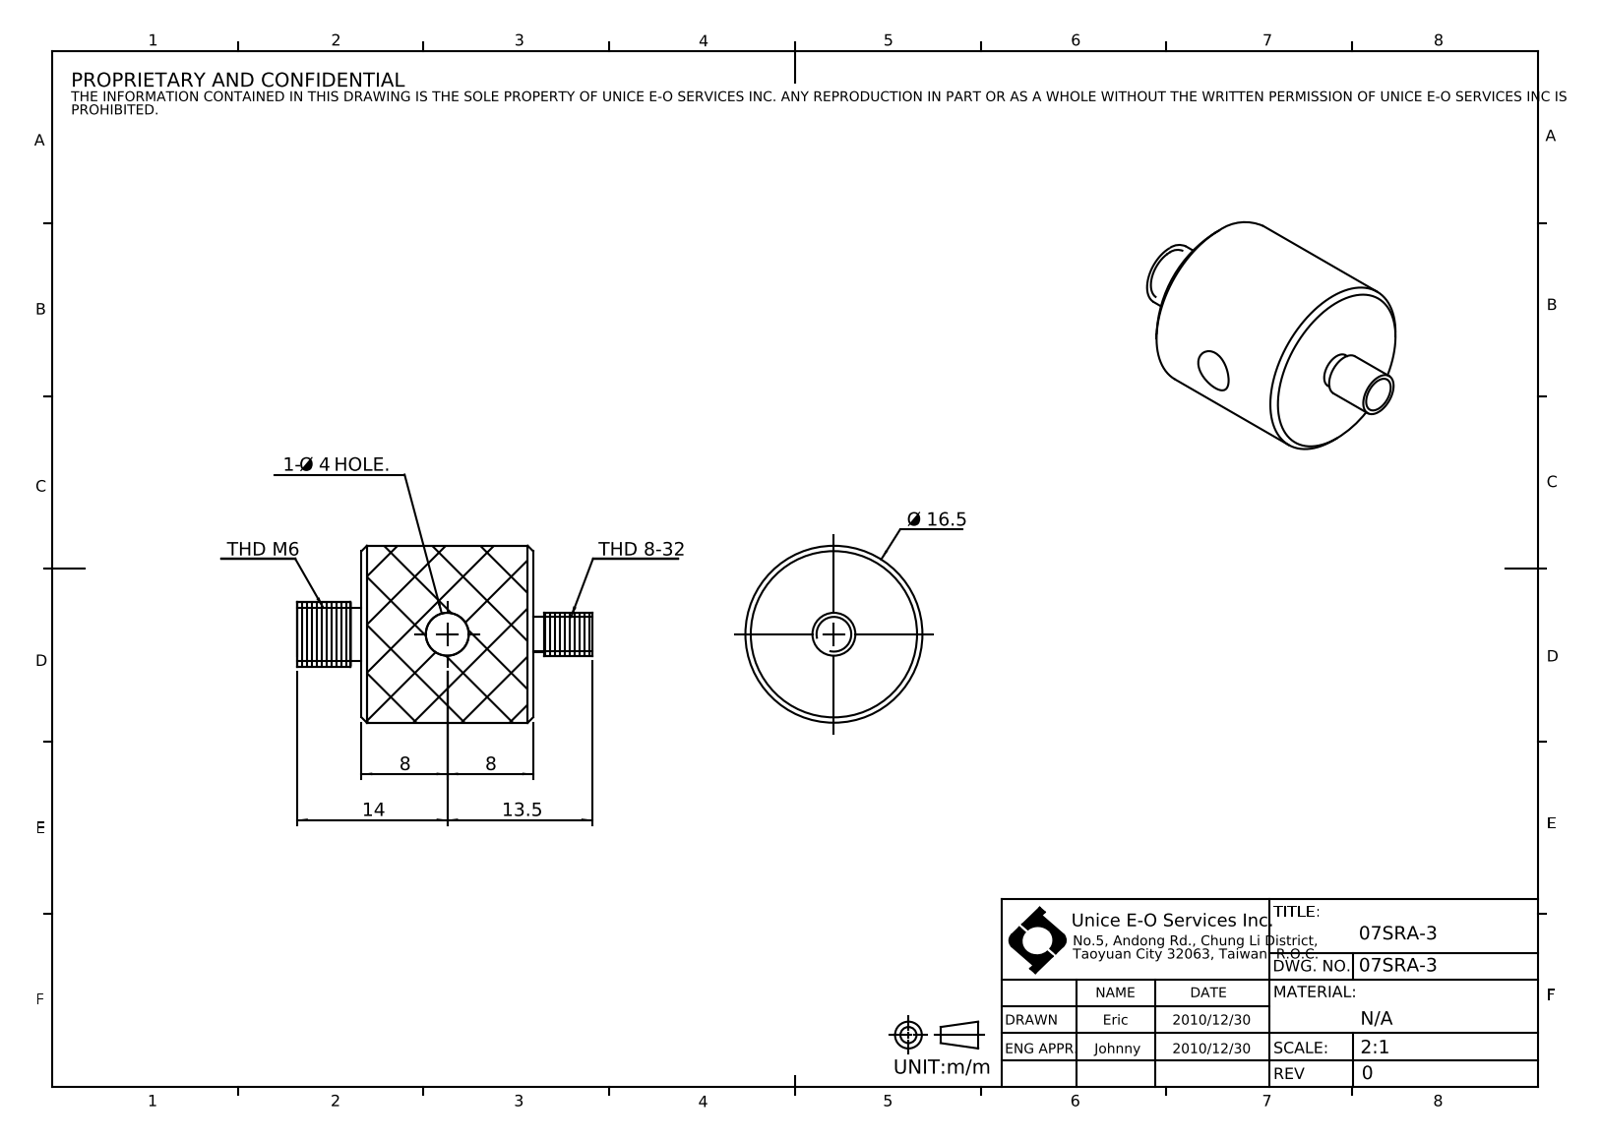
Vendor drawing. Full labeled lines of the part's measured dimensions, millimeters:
Part name (STEP PRODUCT): 07SRA-3
STEP written by: SolidWorks 2016 (CONFIG_CONTROL_DESIGN)
Units: millimetres
Bodies: 1 solid, 22 faces (6 planar, 12 cylindrical, 4 other)
Overall size (bounding box): 27.5 × 16.5 × 16.5
Volume: 3 429 mm³ · Surface area: 1 607 mm²
Round holes (diameter × count): ⌀4 ×1
Round bosses / shafts (diameter × count): ⌀16.5 ×1, ⌀6 ×1, ⌀5 ×1, ⌀4 ×1, ⌀3.3 ×1
Main face-to-face distances: 16, 22, 6, 1, 17, 5.5, 21.5, 27.5, 22.5, 5
